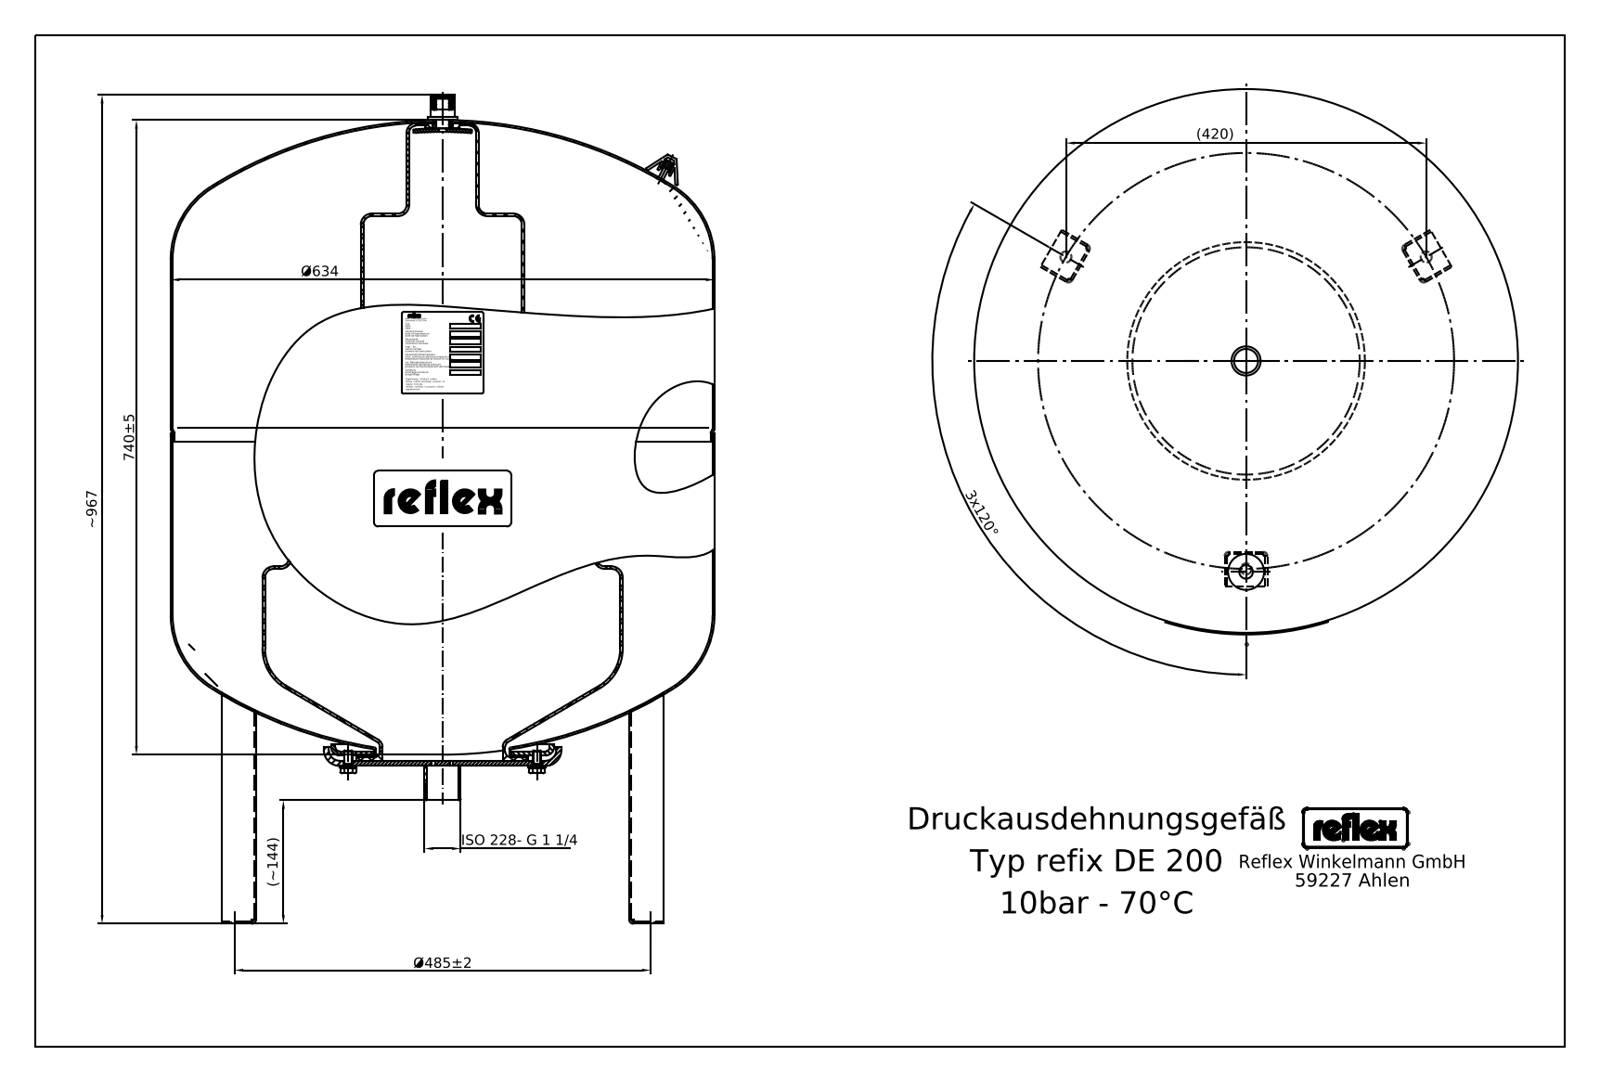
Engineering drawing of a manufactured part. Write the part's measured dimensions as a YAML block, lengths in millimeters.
step_written_by: "Mechanical Desktop 2008 (CONFIG_CONTROL_DESIGN)"
units: millimeters
bodies: {solids: 17, faces: 394, planar: 181, cylindrical: 139, other: 74}
overall_size: [967, 634, 634]
volume: 199400000
surface_area: 3421000
round_holes:
  - {diameter: 13.4, count: 3}
  - {diameter: 14.1, count: 1}
  - {diameter: 157, count: 1}
  - {diameter: 250, count: 1}
round_bosses_or_shafts:
  - {diameter: 10, count: 8}
  - {diameter: 634, count: 1}
  - {diameter: 260, count: 1}
  - {diameter: 230, count: 1}
  - {diameter: 42.4, count: 1}
  - {diameter: 34, count: 1}
  - {diameter: 17.1, count: 1}
  - {diameter: 16, count: 1}
partial_cylinders:
  - {radius: 1, count: 15}
  - {radius: 2.5, count: 15}
  - {radius: 5, count: 15}
  - {radius: 5.62, count: 4}
  - {radius: 2.25, count: 3}
  - {radius: 3.84, count: 2}
  - {radius: 6.75, count: 2}
  - {radius: 9.27, count: 2}
face_to_face_distances: [416, 2.5, 47.5, 169, 585, 6, 175, 591, 45, 50]
hole_center_spacings: [242.5, 420.02]
